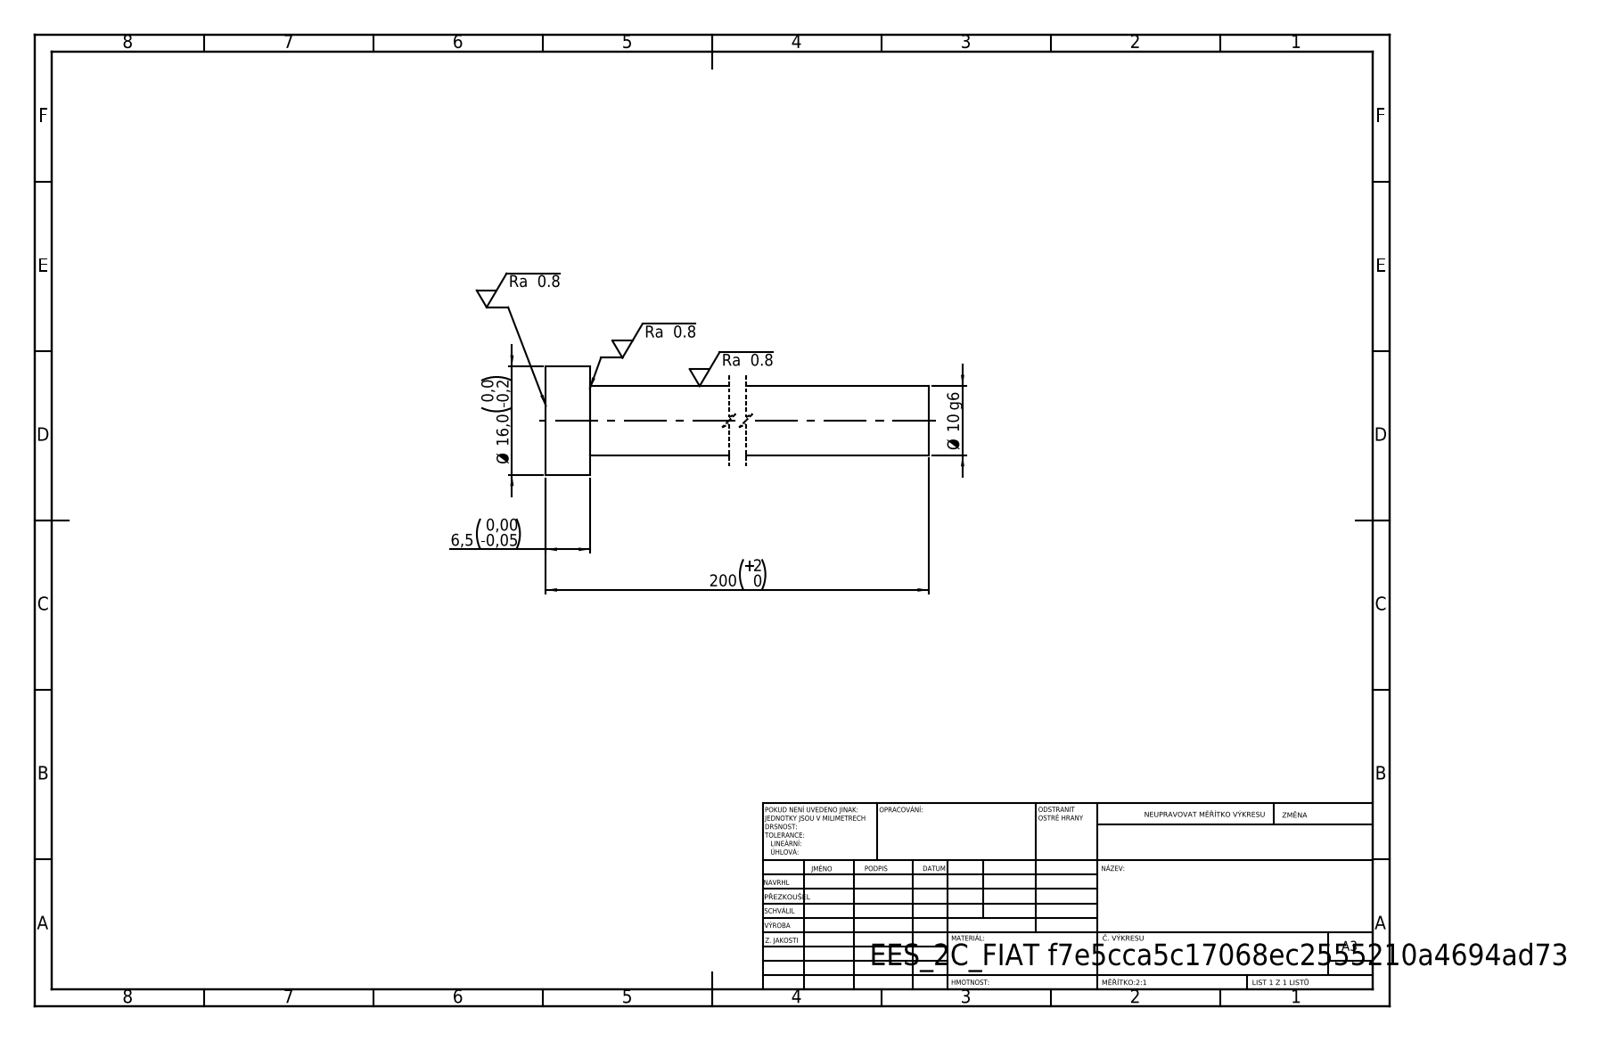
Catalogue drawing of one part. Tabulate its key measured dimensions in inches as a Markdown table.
| quantity | value |
| --- | --- |
| STEP written by | SolidWorks 2019 (CONFIG_CONTROL_DESIGN) |
| units | inches |
| bodies | 1 solid, 7 faces (3 planar, 4 cylindrical, 0 other) |
| overall size | 7.874 × 0.63 × 0.63 |
| volume | 1.045 in³ |
| surface area | 10.74 in² |
| round bosses / shafts (diameter × count) | 0.63 × 1, 0.402 × 1 |
| main face-to-face distances | 0.256, 7.874, 7.618 |
